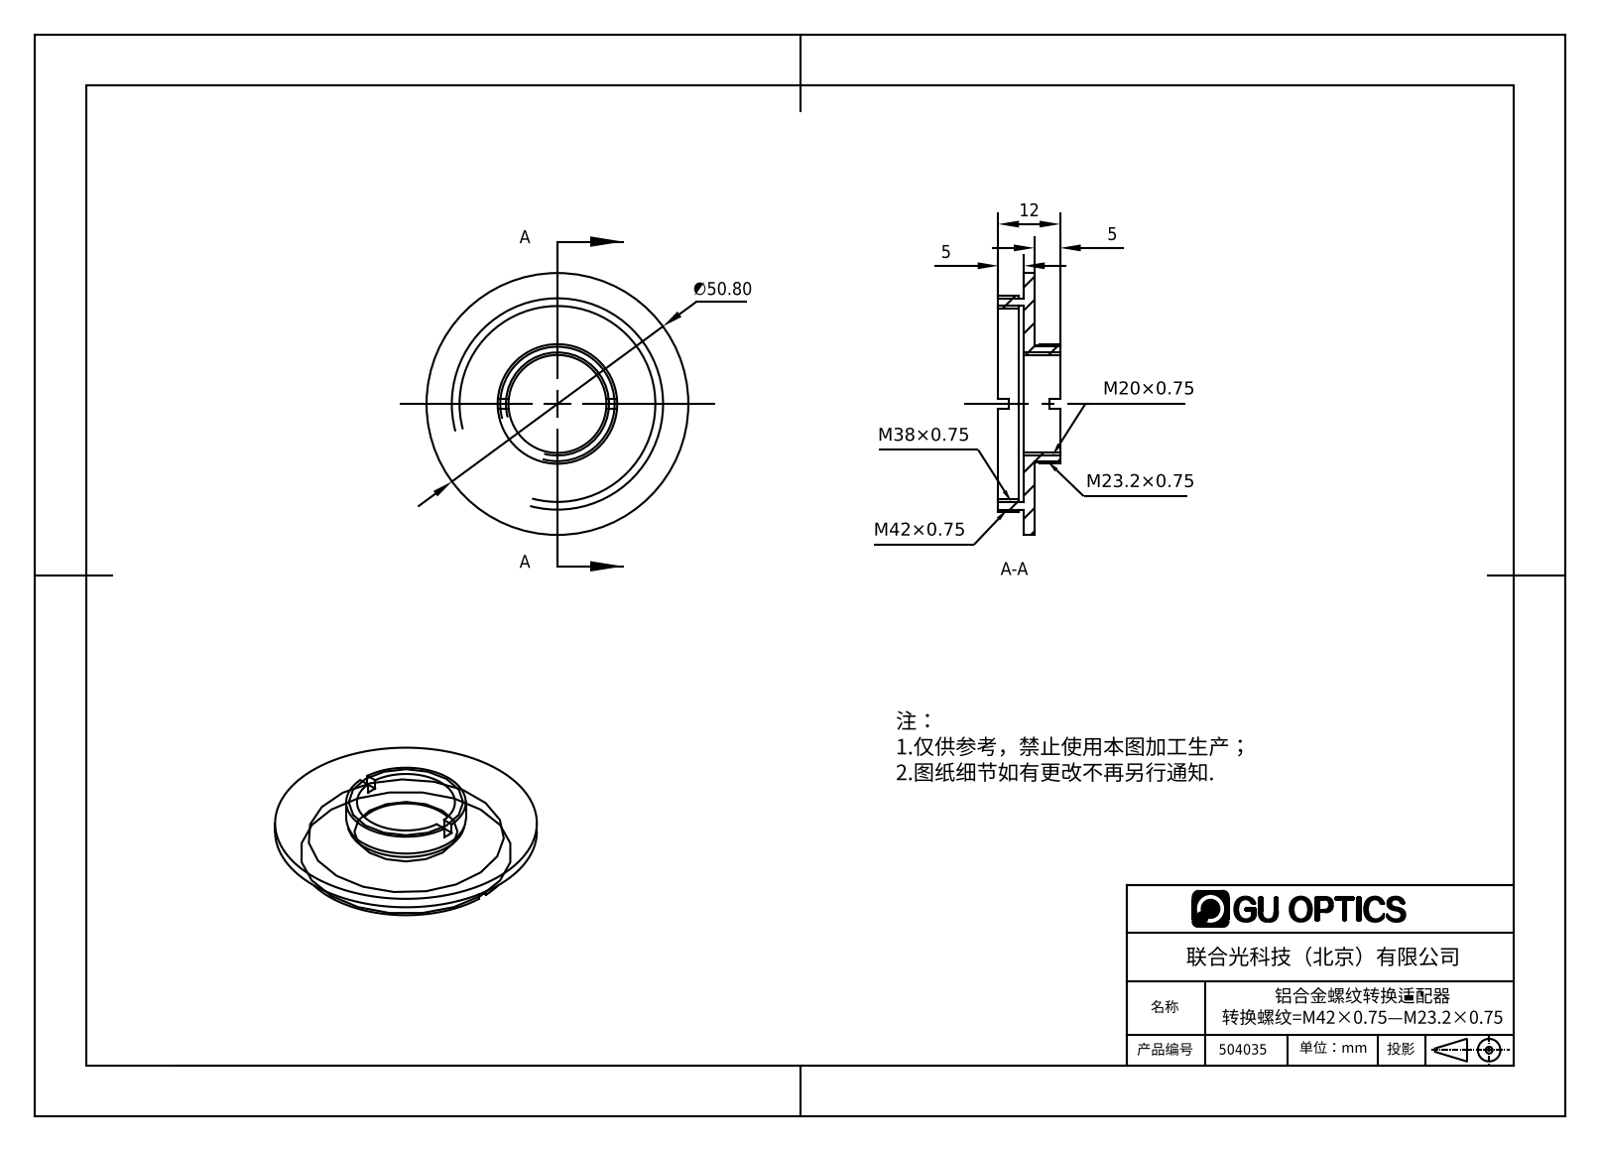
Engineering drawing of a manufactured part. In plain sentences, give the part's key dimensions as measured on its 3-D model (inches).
The part is named "504035". Its 3-D file was written by "SolidWorks 2016 (AUTOMOTIVE_DESIGN)". It is 1 solid with 38 faces: 22 planar, 16 cylindrical and 0 other. Overall it measures 2 by 2 by 0.472 inches. Its volume is 0.338 cubic inches and its surface area 9.519 square inches. Round holes: 1 of diameter 0.748, 1 of diameter 1.457, 1 of diameter 1.504. Round bosses or shafts: 1 of diameter 2, 1 of diameter 1.654, 1 of diameter 1.614, 1 of diameter 0.913, 1 of diameter 0.894. The main face-to-face distances are 0.079, 0.197, 0.276, 0.118, 0.157, 0.315, 0.039, 0.472, 0.394, 0.236.
